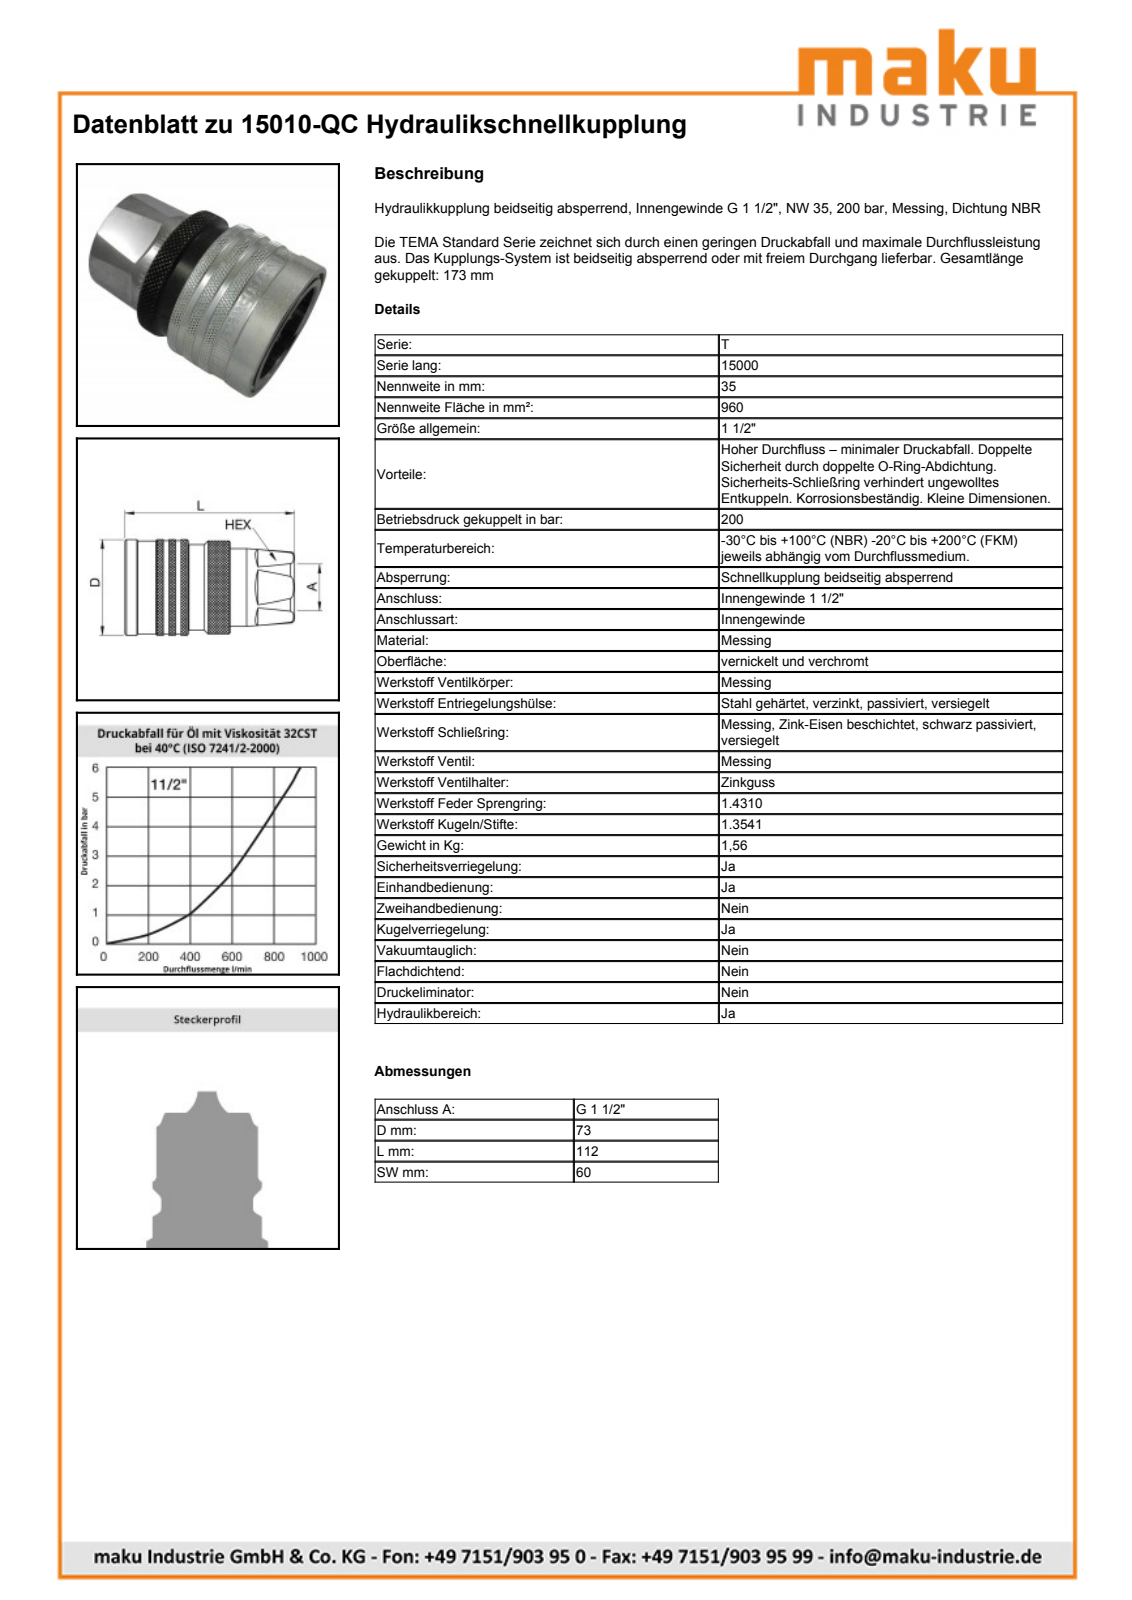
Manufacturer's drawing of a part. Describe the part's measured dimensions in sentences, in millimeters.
The part is named "15010-QC". Its 3-D file was written by "SolidWorks 2009 (AUTOMOTIVE_DESIGN)". It is 1 solid with 139 faces: 33 planar, 46 cylindrical and 60 other. Overall it measures 111.8 by 73 by 73 millimeters. Its volume is 267 547 cubic millimeters and its surface area 52 839 square millimeters. Round holes: 1 of diameter 35, 1 of diameter 44.9, 1 of diameter 48.5, 1 of diameter 48.7, 1 of diameter 49.1, 1 of diameter 51, 1 of diameter 51.5, 1 of diameter 55.7, 1 of diameter 65.5. Round bosses or shafts: 1 of diameter 73, 1 of diameter 71.5, 1 of diameter 71, 1 of diameter 70, 1 of diameter 67, 1 of diameter 66.5, 1 of diameter 60, 1 of diameter 38. The main face-to-face distances are 60, 25, 65.5, 40.5, 55.86, 30.86, 9.64, 7.5, 111.5, 86.5.
